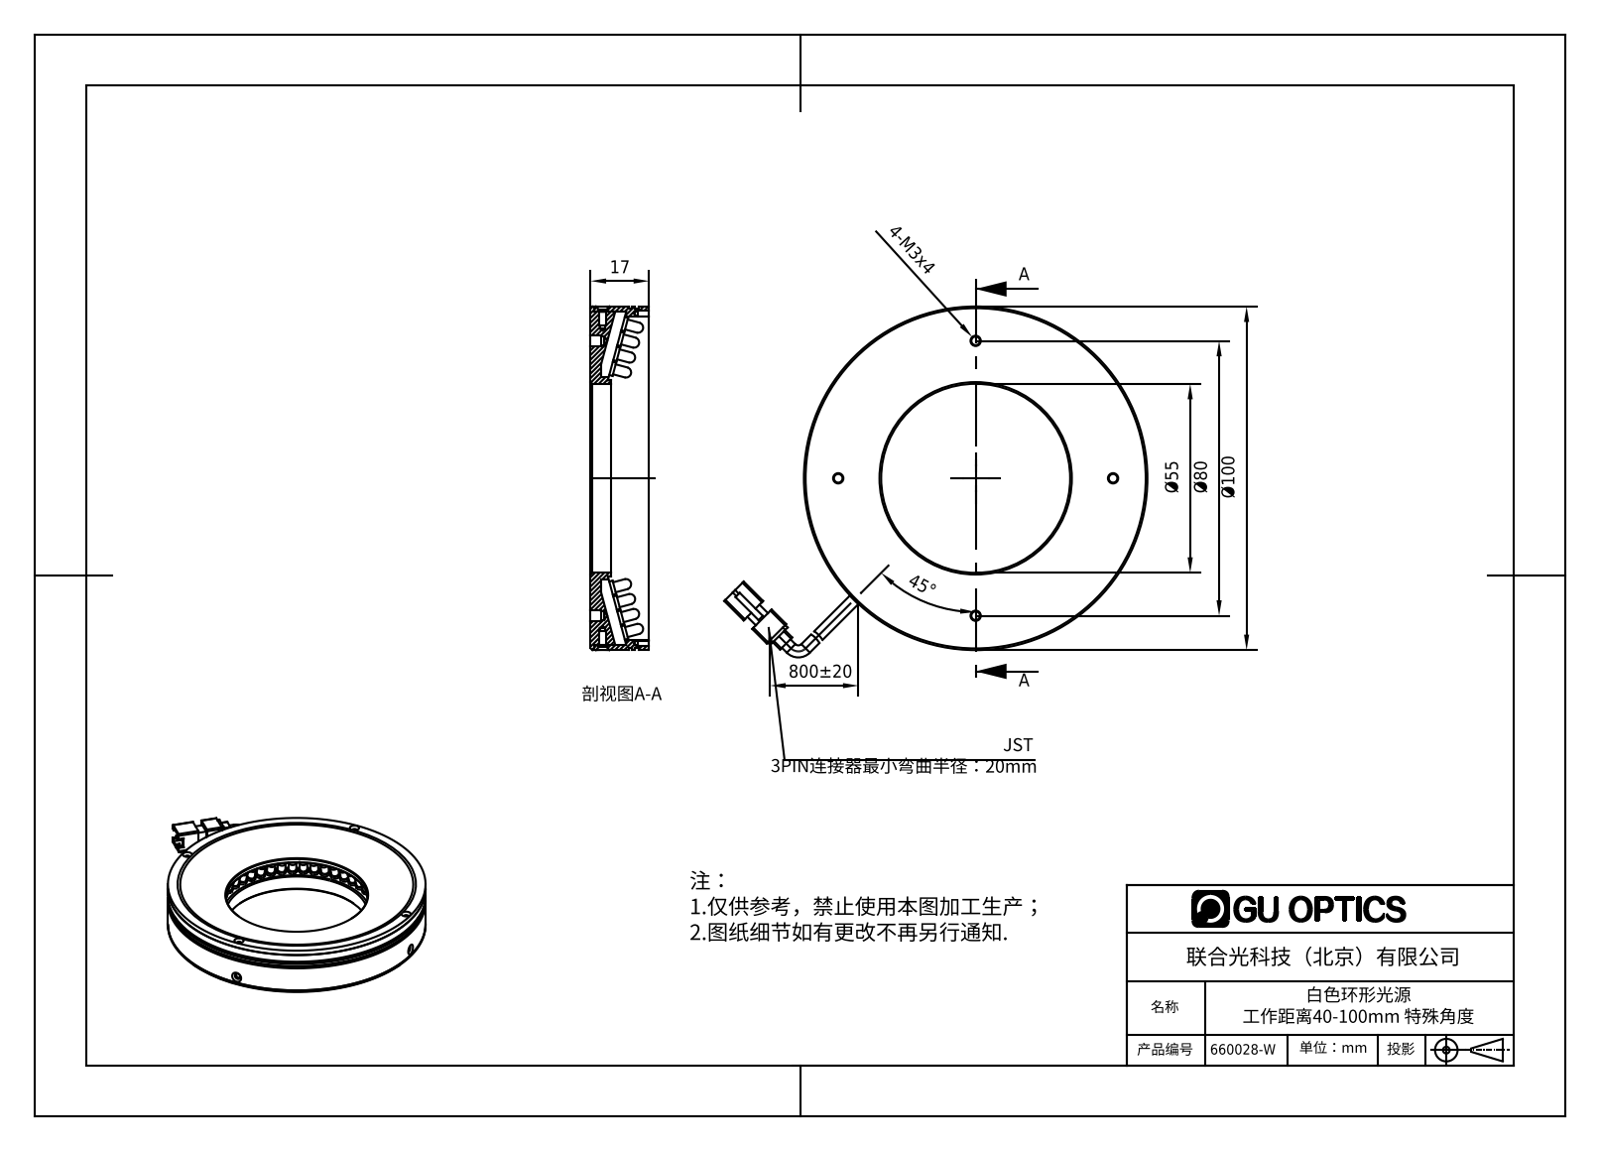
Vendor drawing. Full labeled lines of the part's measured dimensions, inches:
Part name (STEP PRODUCT): 660028-W
STEP written by: SolidWorks 2016 (AUTOMOTIVE_DESIGN)
Units: inches
Bodies: 216 solids, 3870 faces (2609 planar, 980 cylindrical, 281 other)
Overall size (bounding box): 4.85 × 4.021 × 0.884
Volume: 3.55 in³ · Surface area: 106.7 in²
Round holes (diameter × count): ⌀0.063 ×6, ⌀0.049 ×4, ⌀0.067 ×4, ⌀0.098 ×4, ⌀0.118 ×4, ⌀0.138 ×4, ⌀0.079 ×2, ⌀0.094 ×2, ⌀2.165 ×1, ⌀3.701 ×1
Round bosses / shafts (diameter × count): ⌀0.15 ×210, ⌀0.118 ×210, ⌀0.138 ×2, ⌀3.937 ×1, ⌀3.898 ×1, ⌀3.819 ×1, ⌀2.323 ×1, ⌀2.244 ×1
Partial cylindrical surfaces — rounded edges, fillets, slot ends (radius × count): R0.02 ×10, R0.039 ×4, R0.065 ×1, R0.295 ×1
Main face-to-face distances: 0.039, 0.079, 0.669, 0.118, 0.63, 0.02, 0.748, 0.551, 0.709, 0.197
Hole centre spacings: 2.46, 0.315, 1.575, 1.89, 2.227, 2.672, 3.465, 3.15
